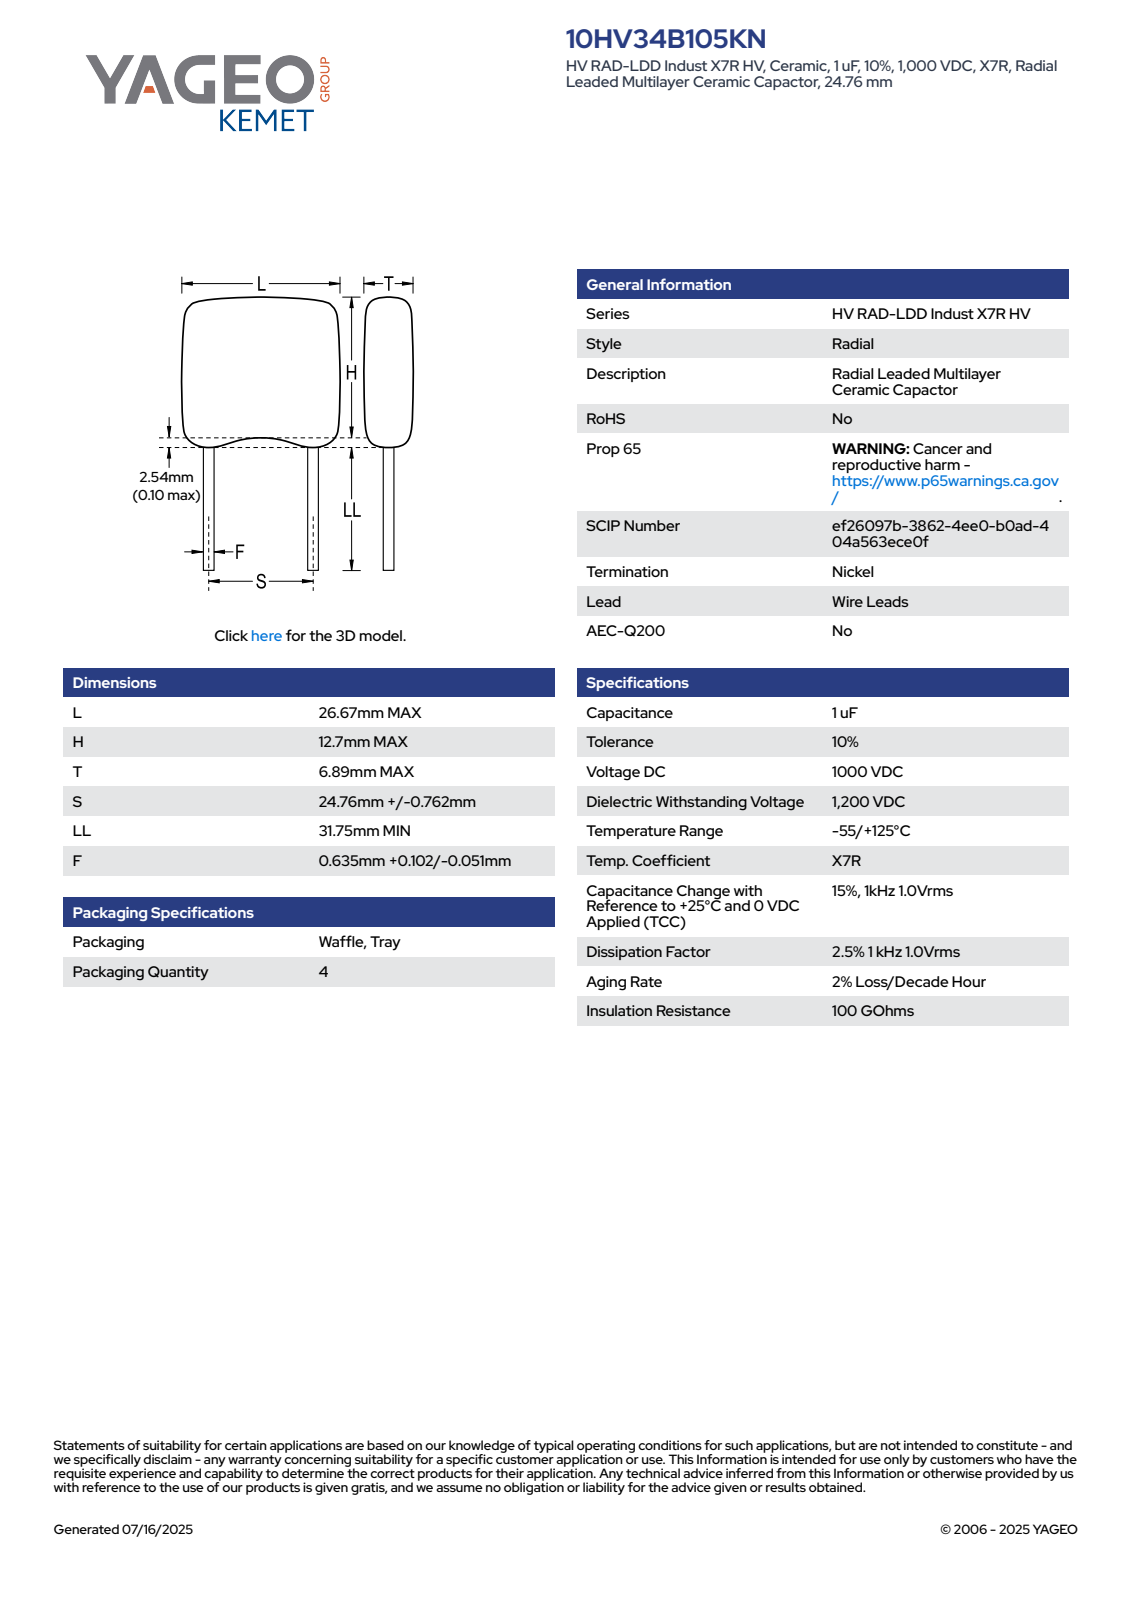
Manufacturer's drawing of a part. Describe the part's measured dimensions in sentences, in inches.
The part is named "CCRM_RCST_HV34_L26.67H12.7T6.89S24.76LL31.75F0.737". Its 3-D file was written by "SolidWorks 2021 (AUTOMOTIVE_DESIGN)". It is 4 solids with 98 faces: 66 planar, 20 cylindrical and 12 other. Overall it measures 1.05 by 0.687 by 0.271 inches. Its volume is 0.147 cubic inches and its surface area 2.01 square inches. Round bosses or shafts: 2 of diameter 0.029. Partial cylindrical surfaces (rounded edges, fillets, slot ends): 8 of radius 0.039, 4 of radius 0.02. The main face-to-face distances are 0.271, 1.05, 0.562, 0.125, 0.687, 0.507, 0.382, 0.18, 0.374, 0.249.
